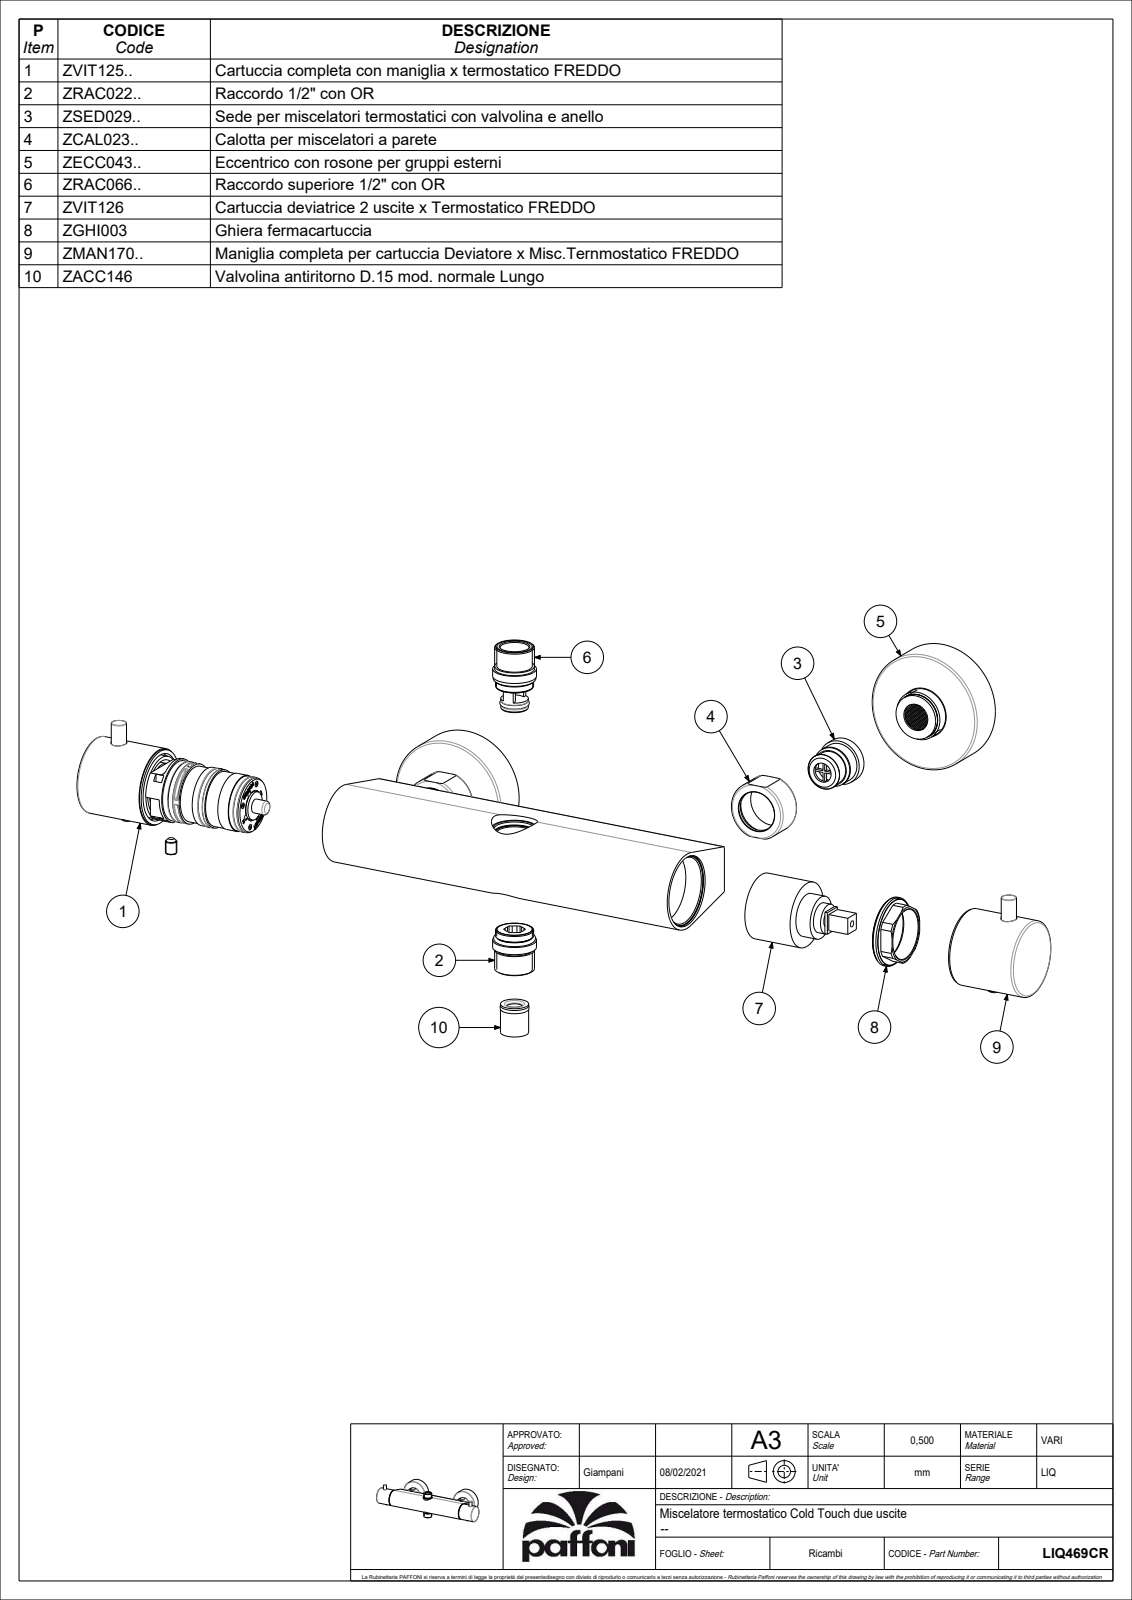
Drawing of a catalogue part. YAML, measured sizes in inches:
part_name: "LIQ469CR"
step_written_by: "CREO PARAMETRIC BY PTC INC, 2020044 (CONFIG_CONTROL_DESIGN)"
units: inches
bodies: {solids: 4, faces: 2930, planar: 1855, cylindrical: 478, other: 597}
overall_size: [11.329, 4.093, 2.579]
volume: 17.59
surface_area: 261.5
round_holes:
  - {diameter: 0.071, count: 4}
  - {diameter: 0.157, count: 4}
  - {diameter: 0.118, count: 3}
  - {diameter: 0.335, count: 3}
  - {diameter: 0.488, count: 3}
  - {diameter: 0.594, count: 3}
  - {diameter: 0.098, count: 2}
  - {diameter: 0.128, count: 2}
  - {diameter: 0.236, count: 2}
  - {diameter: 0.276, count: 2}
  - {diameter: 0.323, count: 2}
  - {diameter: 0.413, count: 2}
round_bosses_or_shafts:
  - {diameter: 0.583, count: 3}
  - {diameter: 2.5, count: 2}
  - {diameter: 1.614, count: 2}
  - {diameter: 1.575, count: 2}
  - {diameter: 1.063, count: 2}
  - {diameter: 0.945, count: 2}
  - {diameter: 0.906, count: 2}
  - {diameter: 0.835, count: 2}
partial_cylinders:
  - {radius: 0.085, count: 86}
  - {radius: 0.066, count: 30}
  - {radius: 0.02, count: 18}
  - {radius: 0.046, count: 8}
  - {radius: 0.165, count: 6}
  - {radius: 0.069, count: 4}
  - {radius: 0.075, count: 4}
  - {radius: 0.047, count: 2}
face_to_face_distances: [0.138, 0.024, 0.124, 0.136, 0.807, 1.457, 0.831, 0.256, 8.228, 0.618]
hole_center_spacings: [0.235, 5.906, 0.197, 0.283, 0.339, 0.472, 0.589, 5.767]
